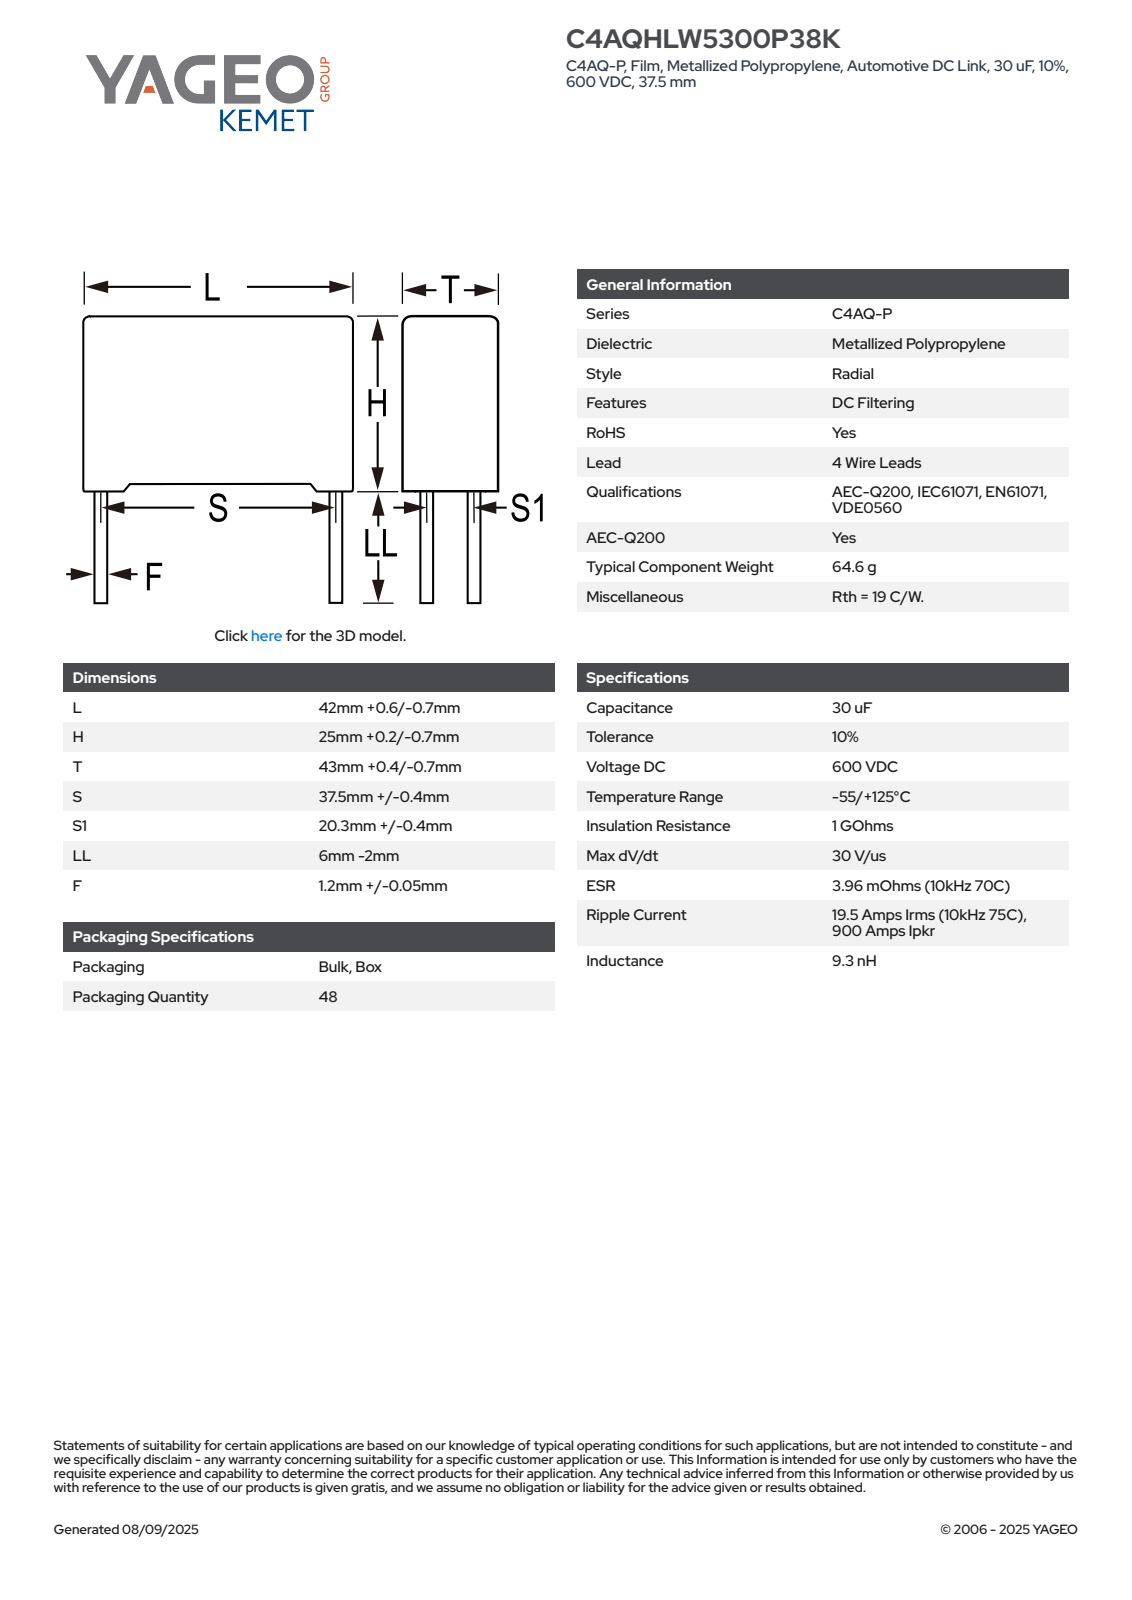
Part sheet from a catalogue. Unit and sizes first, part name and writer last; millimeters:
Units: millimetres
Overall size (bounding box): 43.41 × 42.6 × 29.2
Round bosses / shafts (diameter × count): ⌀1.25 ×4
Main face-to-face distances: 24.46, 42.6, 43.4, 0.74, 25.2, 2.67, 43.41, 39.93, 37.26, 40.73
Volume: 45 451 mm³ · Surface area: 8 246 mm²
Bodies: 4 solids, 91 faces (83 planar, 8 cylindrical, 0 other)
Part name (STEP PRODUCT): CFP_RB4_42X25X43_L42.6H25.2T43.4S37.5S120.3LL4F1.25
STEP written by: SolidWorks 2014 (AUTOMOTIVE_DESIGN)
